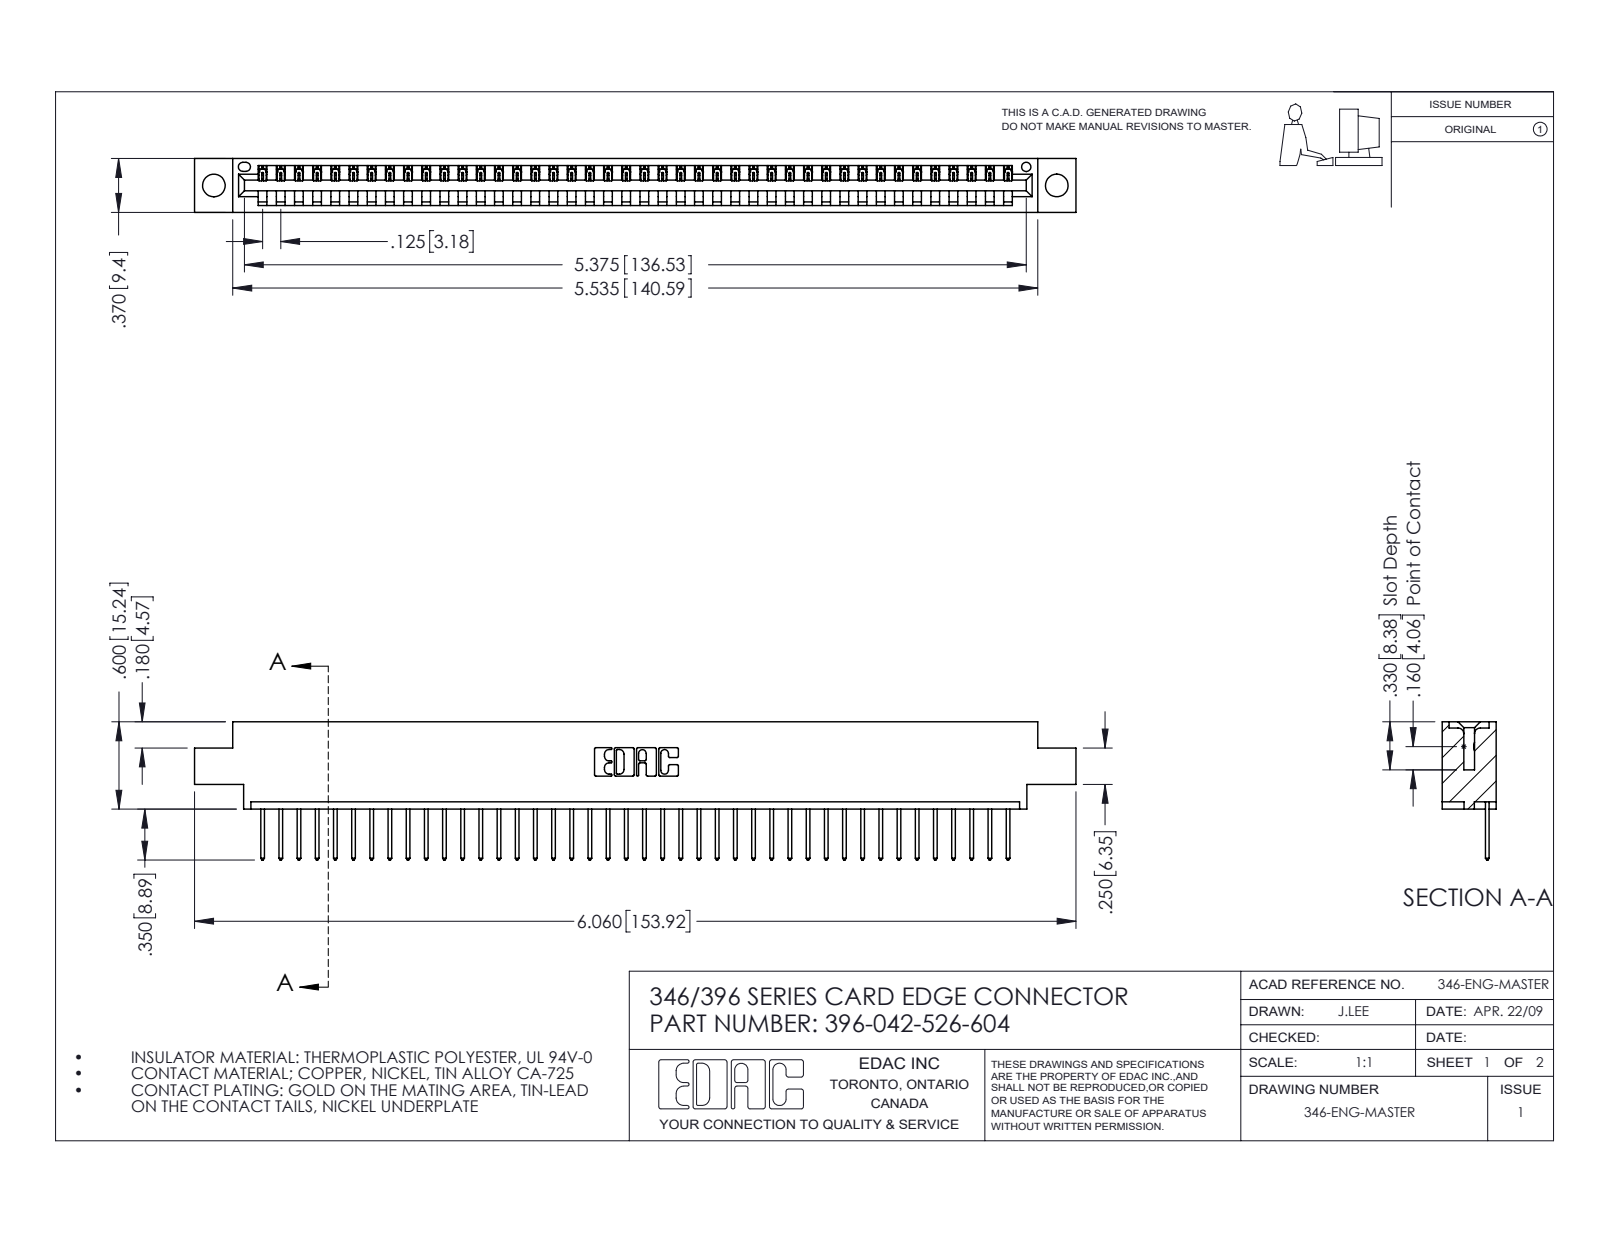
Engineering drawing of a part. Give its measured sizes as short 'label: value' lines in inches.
name: 346 Part_0.170 Offset - 0.156 Dia-TH; 345-292-001_345-293-126; 396-042-526-604
written by: SolidWorks 2016 (CONFIG_CONTROL_DESIGN)
unit: in
bodies: 43 solids, 2562 faces (1760 planar, 802 cylindrical, 0 other)
size: 6.06 × 0.95 × 0.37
volume: 0.882 in³; area: 27.89 in²
holes: 2× ⌀0.156, 1× ⌀0.064
rounds: 84× R0.006, 84× R0.01, 22× R0.01, 6× R0.007, 6× R0.031, 3× R0.026, 2× R0.031, 2× R0.04
face distances: 0.048, 0.322, 0.37, 0.25, 0.072, 0.298, 0.025, 0.148, 0.222, 0.1
hole spacings: 0.246, 5.586, 5.795
